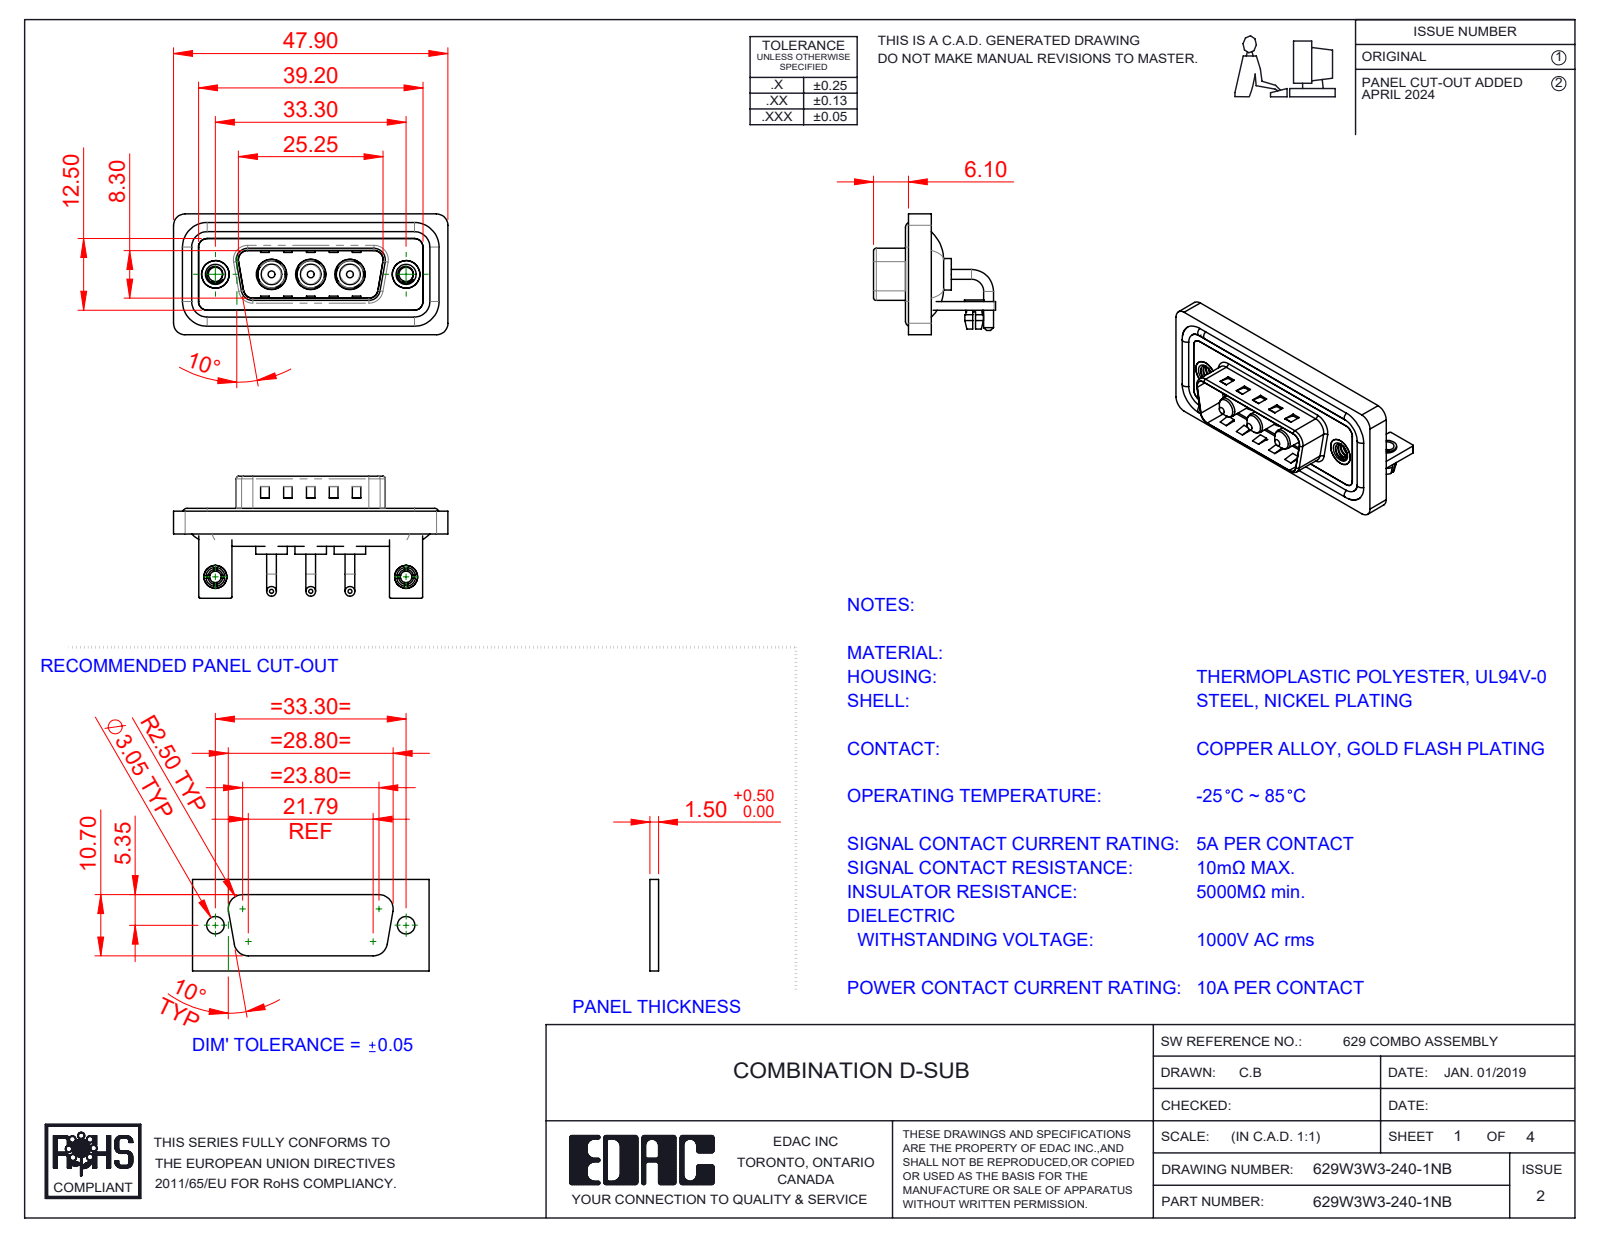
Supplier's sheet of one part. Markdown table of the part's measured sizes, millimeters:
| quantity | value |
| --- | --- |
| part name | 629Combo Board Lock; 629Combo Stabilizer Bracket; Power Pin_10A RA; 629Combo Threaded Rivet_B (+5 more) |
| STEP written by | SolidWorks 2023 (CONFIG_CONTROL_DESIGN) |
| units | millimeters |
| bodies | 17 solids, 706 faces (275 planar, 297 cylindrical, 134 other) |
| overall size | 47.9 × 21.3 × 21.1 |
| volume | 5 912 mm³ |
| surface area | 9 682 mm² |
| round holes (diameter × count) | 2.5 × 4, 4.85 × 3, 5.3 × 3, 2 × 2, 3.2 × 2, 4 × 2, 4.8 × 2, 5 × 2 |
| round bosses / shafts (diameter × count) | 1.7 × 6, 1.6 × 4, 5.5 × 3, 5.2 × 3, 4.75 × 3, 3.75 × 3, 3.6 × 3, 4.9 × 2 |
| partial cylindrical surfaces (radius × count) | 2 × 21, 1.5 × 18, 0.25 × 16, 0.5 × 9, 1.6 × 8, 0.6 × 4, 0.65 × 4, 0.9 × 4 |
| main face-to-face distances | 0.4, 1.5, 0.8, 2.9, 1.1, 2.1, 3.7, 1.6, 1.2, 4.5 |
| hole center spacings | 6.85, 9.8, 16.65, 23.5, 33.3, 13.7 |
